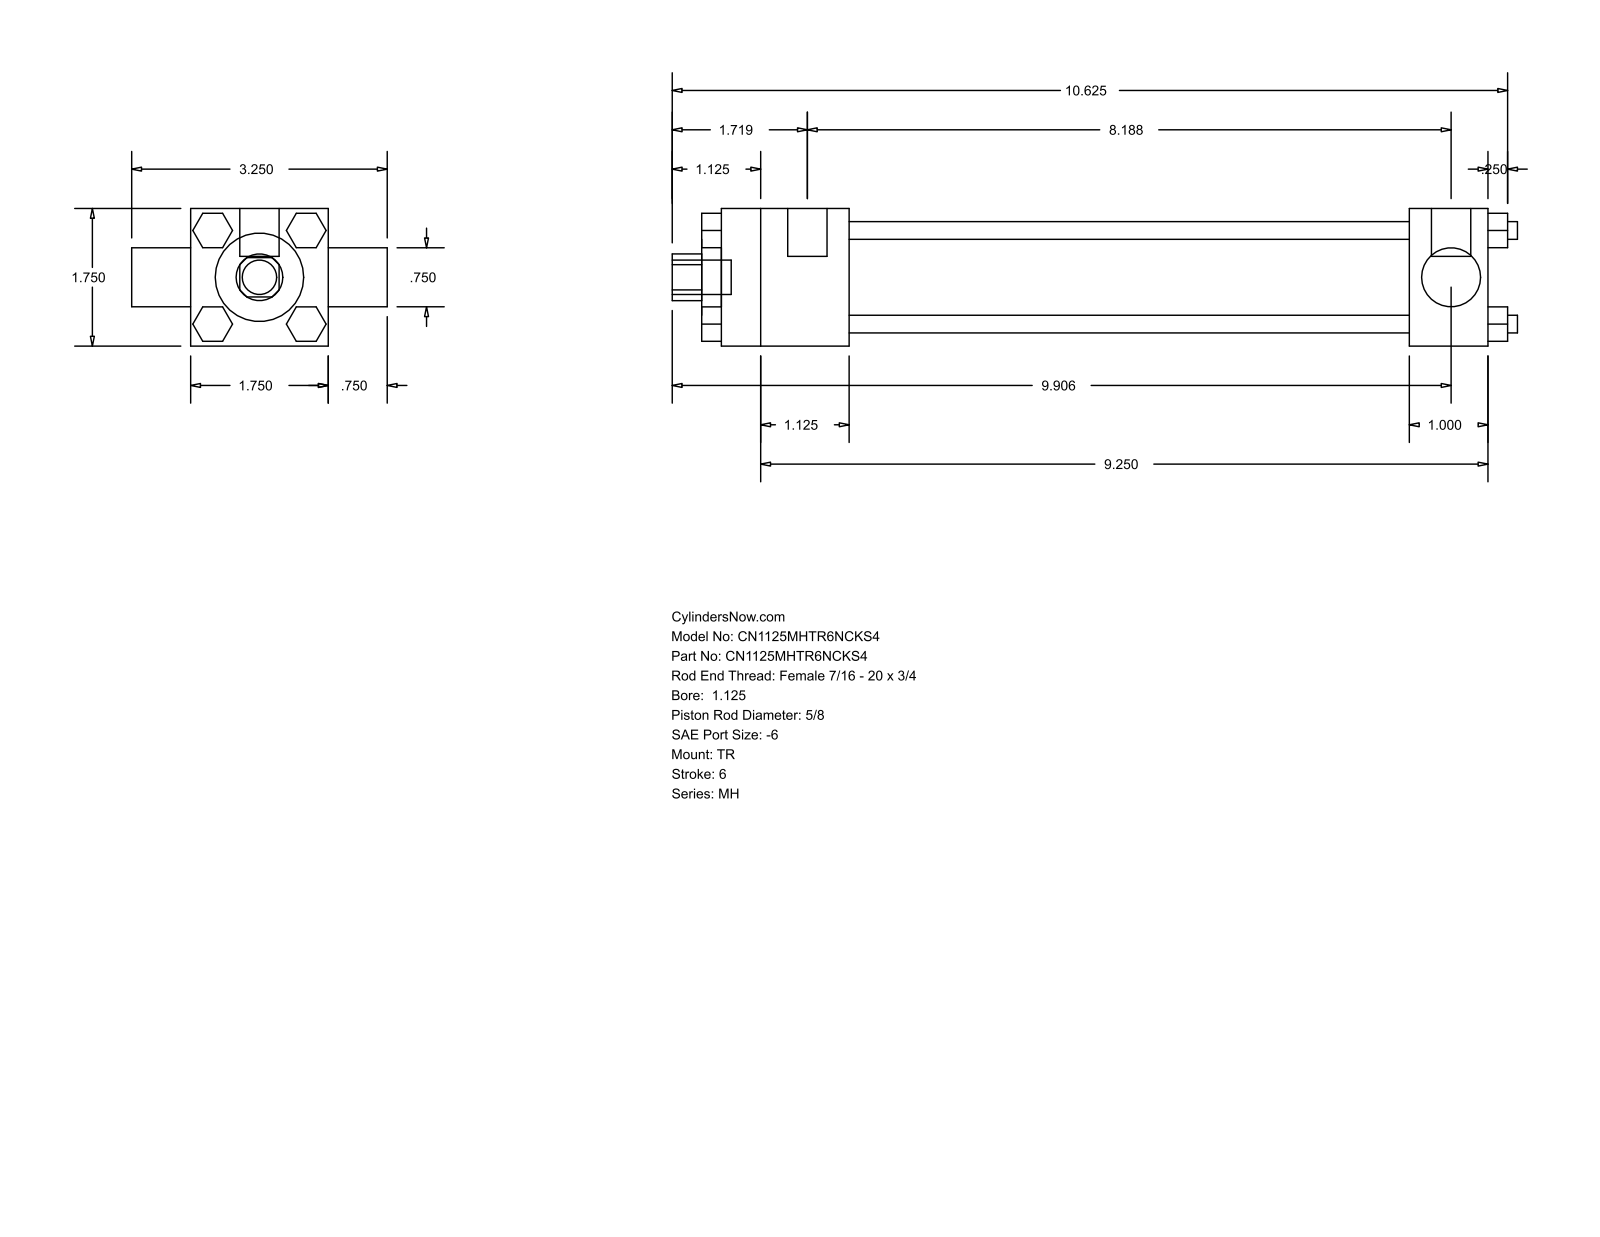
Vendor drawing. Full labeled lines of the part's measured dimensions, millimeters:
Part name (STEP PRODUCT): MH_TR__0112_0.625
STEP written by: GSSL Pune (CONFIG_CONTROL_DESIGN)
Units: millimetres
Bodies: 0 solids, 120 faces (92 planar, 28 cylindrical, 0 other)
Overall size (bounding box): 273.05 × 82.55 × 44.45
Round holes (diameter × count): ⌀15.88 ×1, ⌀19.05 ×1, ⌀28.57 ×1, ⌀34.92 ×1
Round bosses / shafts (diameter × count): ⌀5.71 ×4, ⌀5.56 ×3, ⌀12.7 ×2, ⌀11.11 ×1
Partial cylindrical surfaces — rounded edges, fillets, slot ends (radius × count): R7.54 ×1
Main face-to-face distances: 44.46, 11.11, 180.97, 206.37, 25.4, 41.27, 222.24, 247.64, 47.62, 6.35
